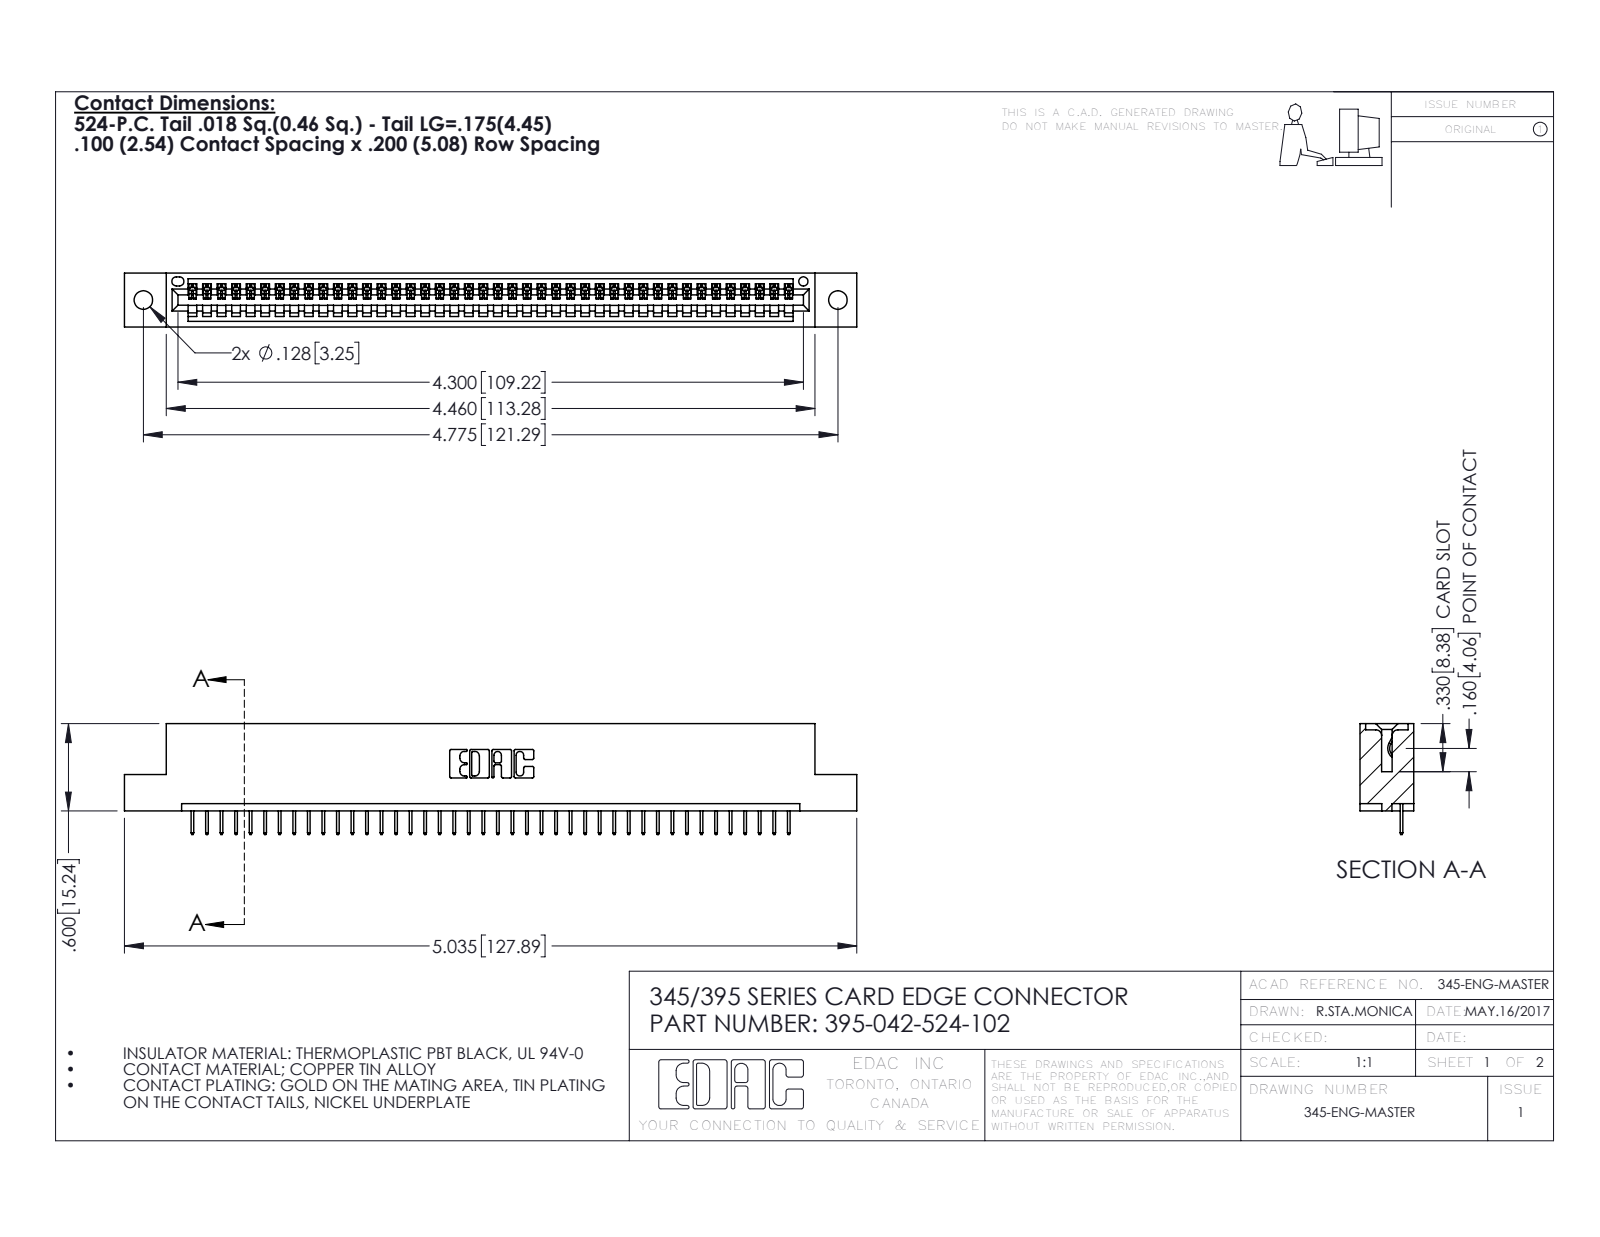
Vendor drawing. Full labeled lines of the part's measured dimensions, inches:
Part name (STEP PRODUCT): 345-292-001_345-293-124; 345 Part_Flush Mounting Lugs - 0.128 Dia; 395-042-524-102
STEP written by: SolidWorks 2016 (CONFIG_CONTROL_DESIGN)
Units: inches
Bodies: 43 solids, 2730 faces (2012 planar, 718 cylindrical, 0 other)
Overall size (bounding box): 5.035 × 0.762 × 0.37
Volume: 0.729 in³ · Surface area: 23.36 in²
Round holes (diameter × count): ⌀0.128 ×2, ⌀0.064 ×1
Partial cylindrical surfaces — rounded edges, fillets, slot ends (radius × count): R0.006 ×84, R0.01 ×22, R0.007 ×6, R0.031 ×6, R0.026 ×3, R0.031 ×2, R0.04 ×2, R0.014 ×1
Main face-to-face distances: 0.298, 0.072, 0.37, 0.2, 0.098, 0.272, 0.025, 0.225, 0.072, 0.149
Hole centre spacings: 0.27, 4.539, 4.775
